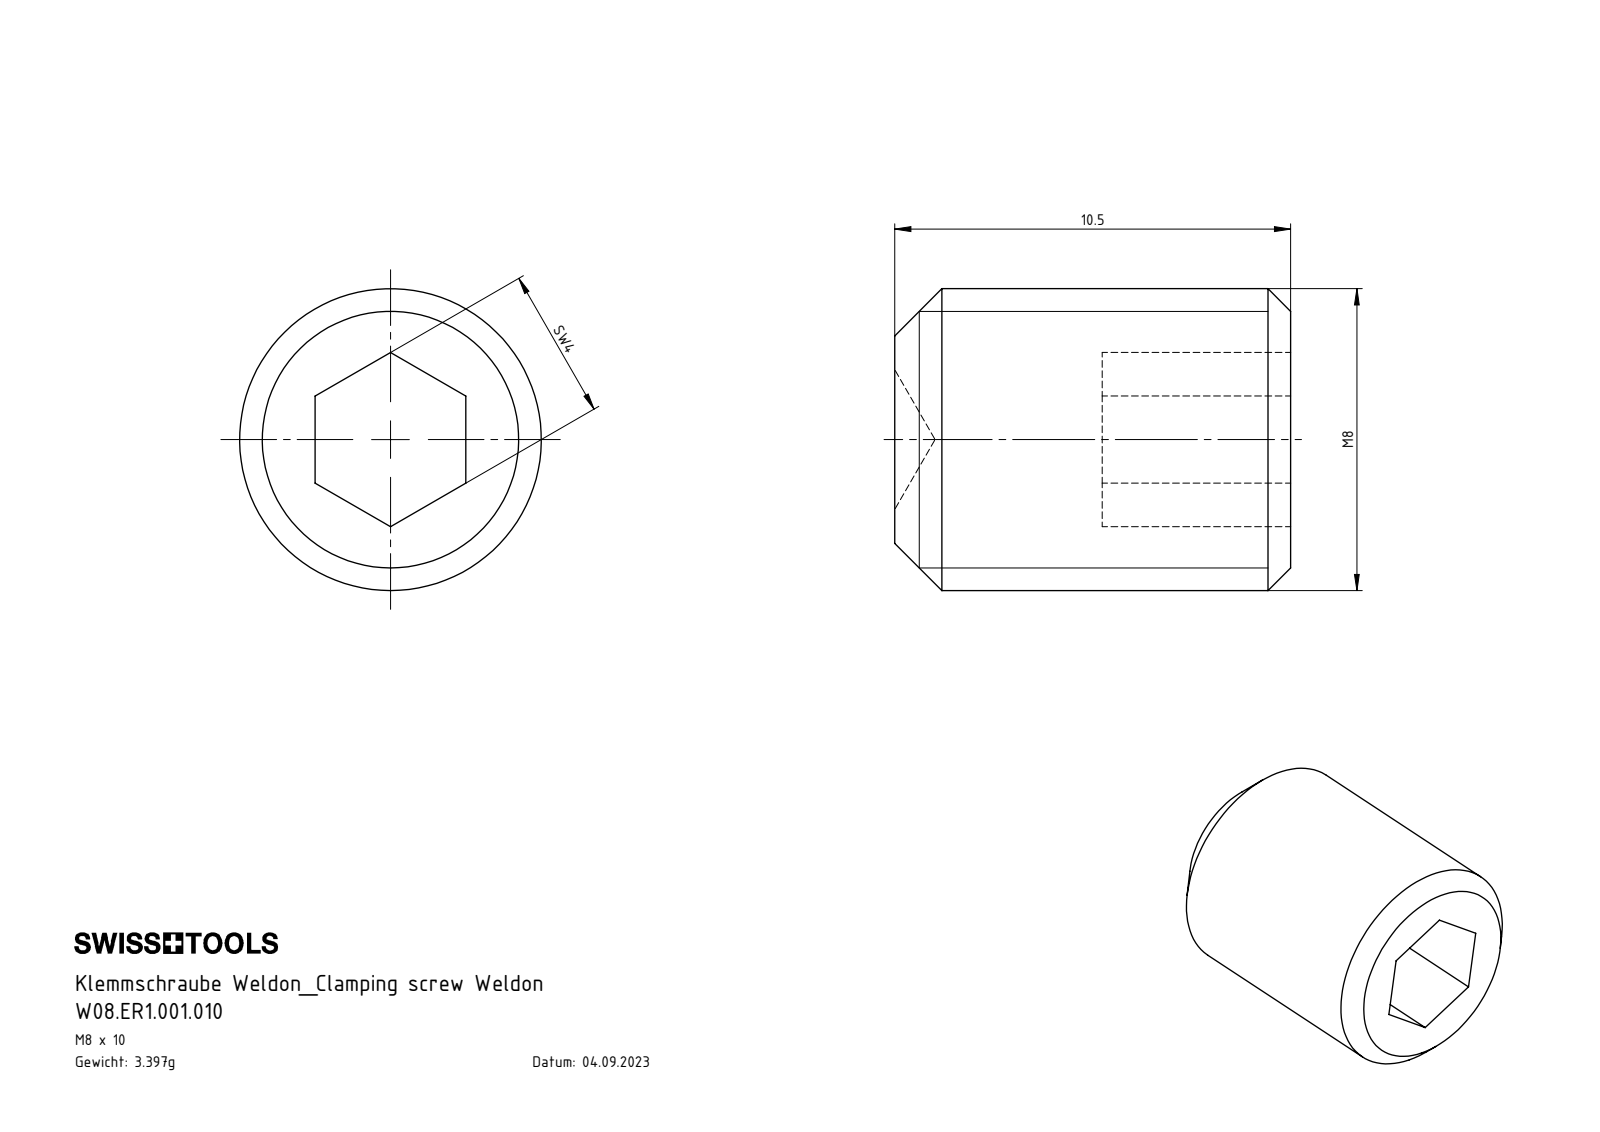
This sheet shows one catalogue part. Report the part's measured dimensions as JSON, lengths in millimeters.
{"part_name": "W08.ER1.001.010", "step_written_by": "SolidWorks 2017 (AUTOMOTIVE_DESIGN)", "units": "millimeters", "bodies": {"solids": 1, "faces": 17, "planar": 9, "cylindrical": 2, "other": 6}, "overall_size": [10.5, 8, 8], "volume_mm3": 433, "surface_area_mm2": 406, "round_bosses_or_shafts": [[8, 1]], "face_to_face_distances": [4, 5, 10.5, 5.5]}
